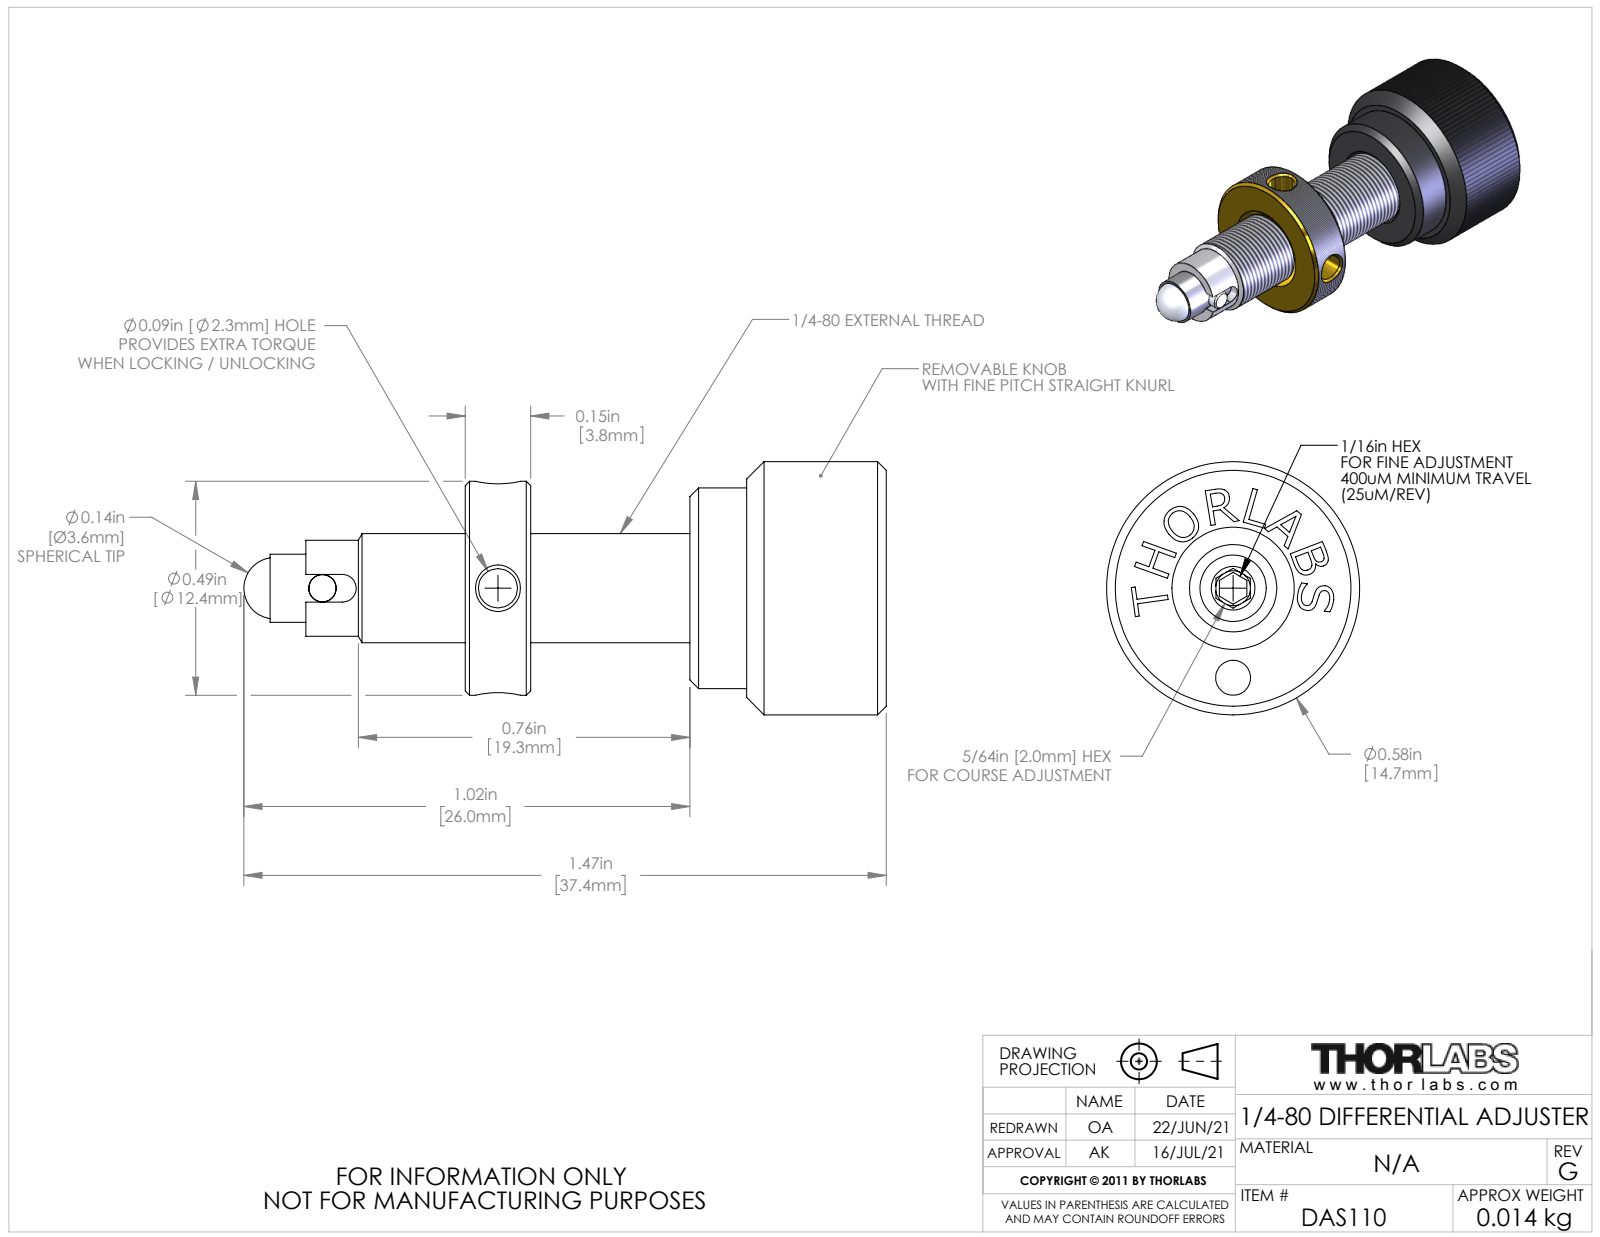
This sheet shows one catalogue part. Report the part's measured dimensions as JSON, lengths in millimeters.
{"part_name": "8650-E0W", "step_written_by": "SolidWorks 2018 (AUTOMOTIVE_DESIGN)", "units": "millimeters", "bodies": {"solids": 8, "faces": 287, "planar": 124, "cylindrical": 65, "other": 98}, "overall_size": [37.4, 14.7, 14.7], "volume_mm3": 2440, "surface_area_mm2": 3042, "round_holes": [[2.3, 2], [1.6, 1], [1.8, 1], [2, 1], [2.5, 1], [3, 1], [3.6, 1], [3.9, 1], [4, 1], [5.3, 1], [6.4, 1], [7.4, 1]], "round_bosses_or_shafts": [[14.7, 1], [12.4, 1], [11.7, 1], [5.6, 1], [5.3, 1], [5, 1], [4, 1], [4, 1]], "partial_cylinders_radius": [[0.8, 1]], "face_to_face_distances": [3.8, 20.7, 24.5, 13.1, 13.8, 11.4, 9.3, 6.9, 4.6, 17.7], "hole_center_spacings": [5.2, 10.2]}
